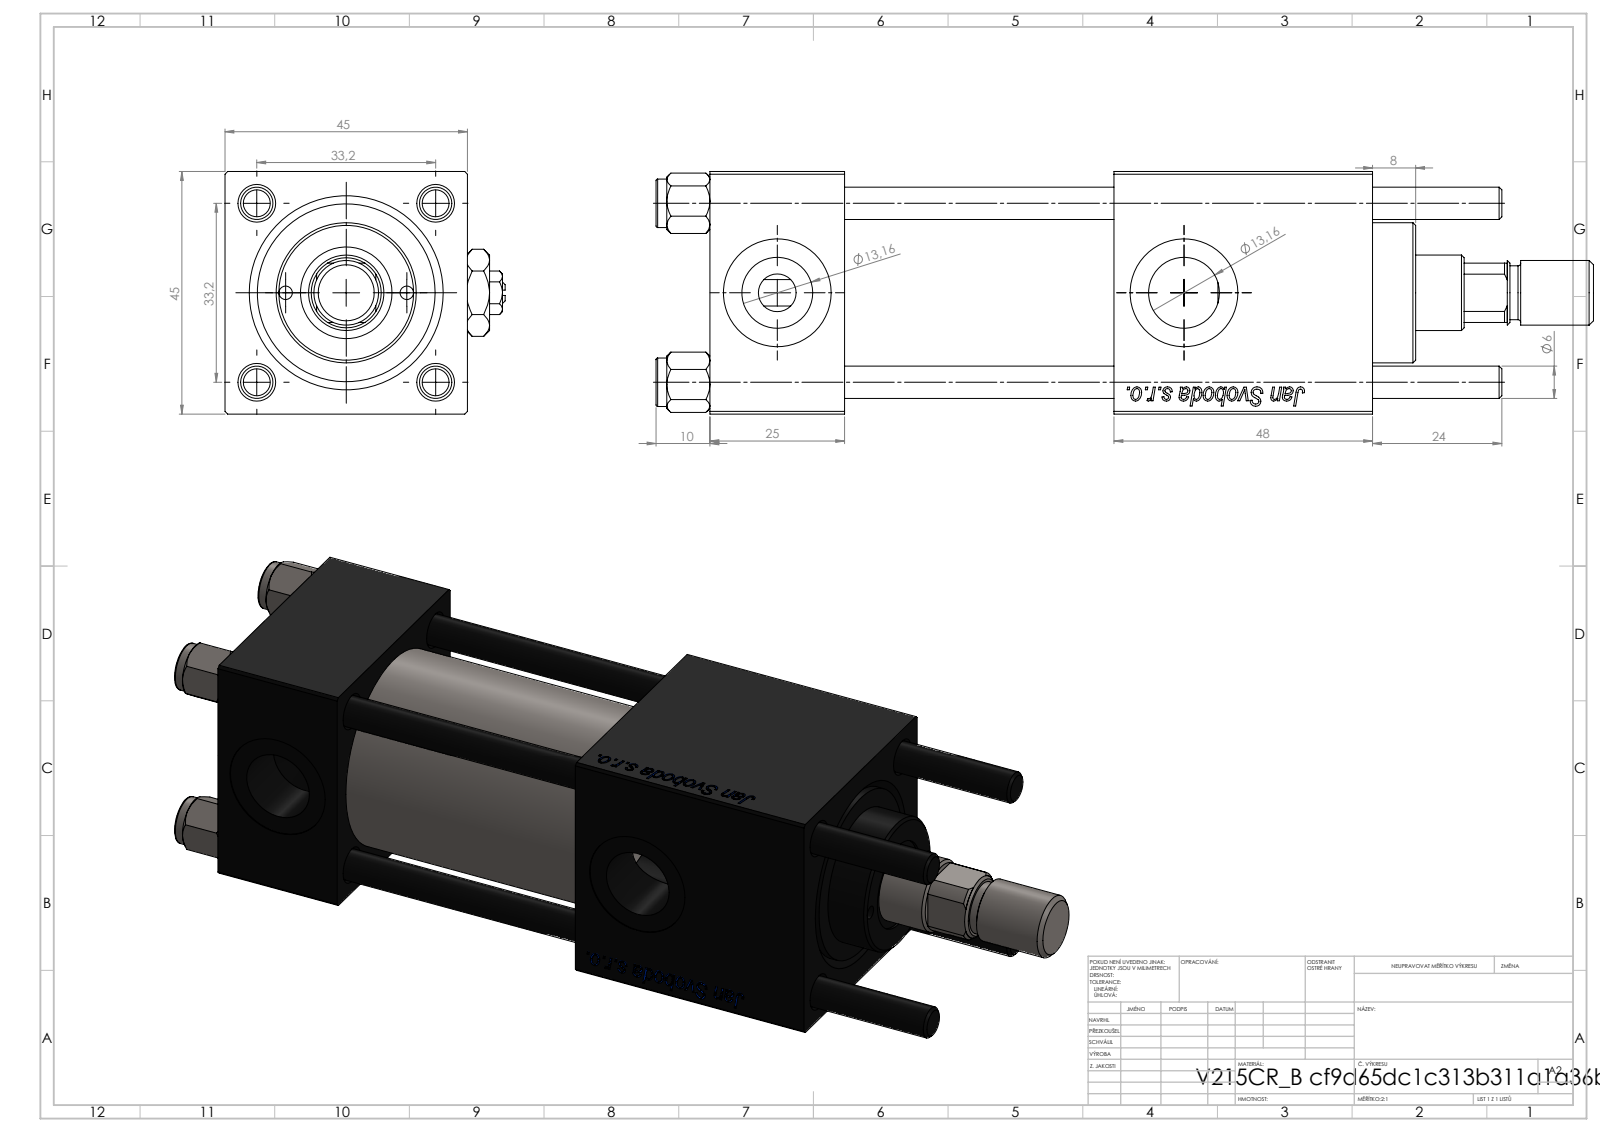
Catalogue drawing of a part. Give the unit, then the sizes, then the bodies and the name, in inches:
Units: inches
Overall size (bounding box): 6.85 × 2.047 × 1.772
Round holes (diameter × count): ⌀0.236 ×4, ⌀0.098 ×2, ⌀0.276 ×2, ⌀0.518 ×2, ⌀0.787 ×2, ⌀0.256 ×1, ⌀0.551 ×1, ⌀0.669 ×1, ⌀0.945 ×1, ⌀1.26 ×1, ⌀1.299 ×1
Round bosses / shafts (diameter × count): ⌀0.354 ×4, ⌀1.496 ×1, ⌀1.024 ×1, ⌀0.472 ×1, ⌀0.394 ×1
Partial cylindrical surfaces — rounded edges, fillets, slot ends (radius × count): R0.256 ×1
Main face-to-face distances: 1.772, 0.984, 4.843, 3.858, 1.969, 2.953, 1.89, 3.713, 2.728, 0.76
Hole centre spacings: 0.687, 0.924, 1.276, 1.307, 0.443, 1.848, 0.886, 2.972
Volume: 12.15 in³ · Surface area: 115.8 in²
Bodies: 13 solids, 1228 faces (460 planar, 92 cylindrical, 676 other)
Part name (STEP PRODUCT): V215CR_VCP_B; Zatka_pro_OIL_PORT; V215CR_B_TYCINKA; V215_VC_A (+3 more)
STEP written by: SolidWorks 2019 (CONFIG_CONTROL_DESIGN)
